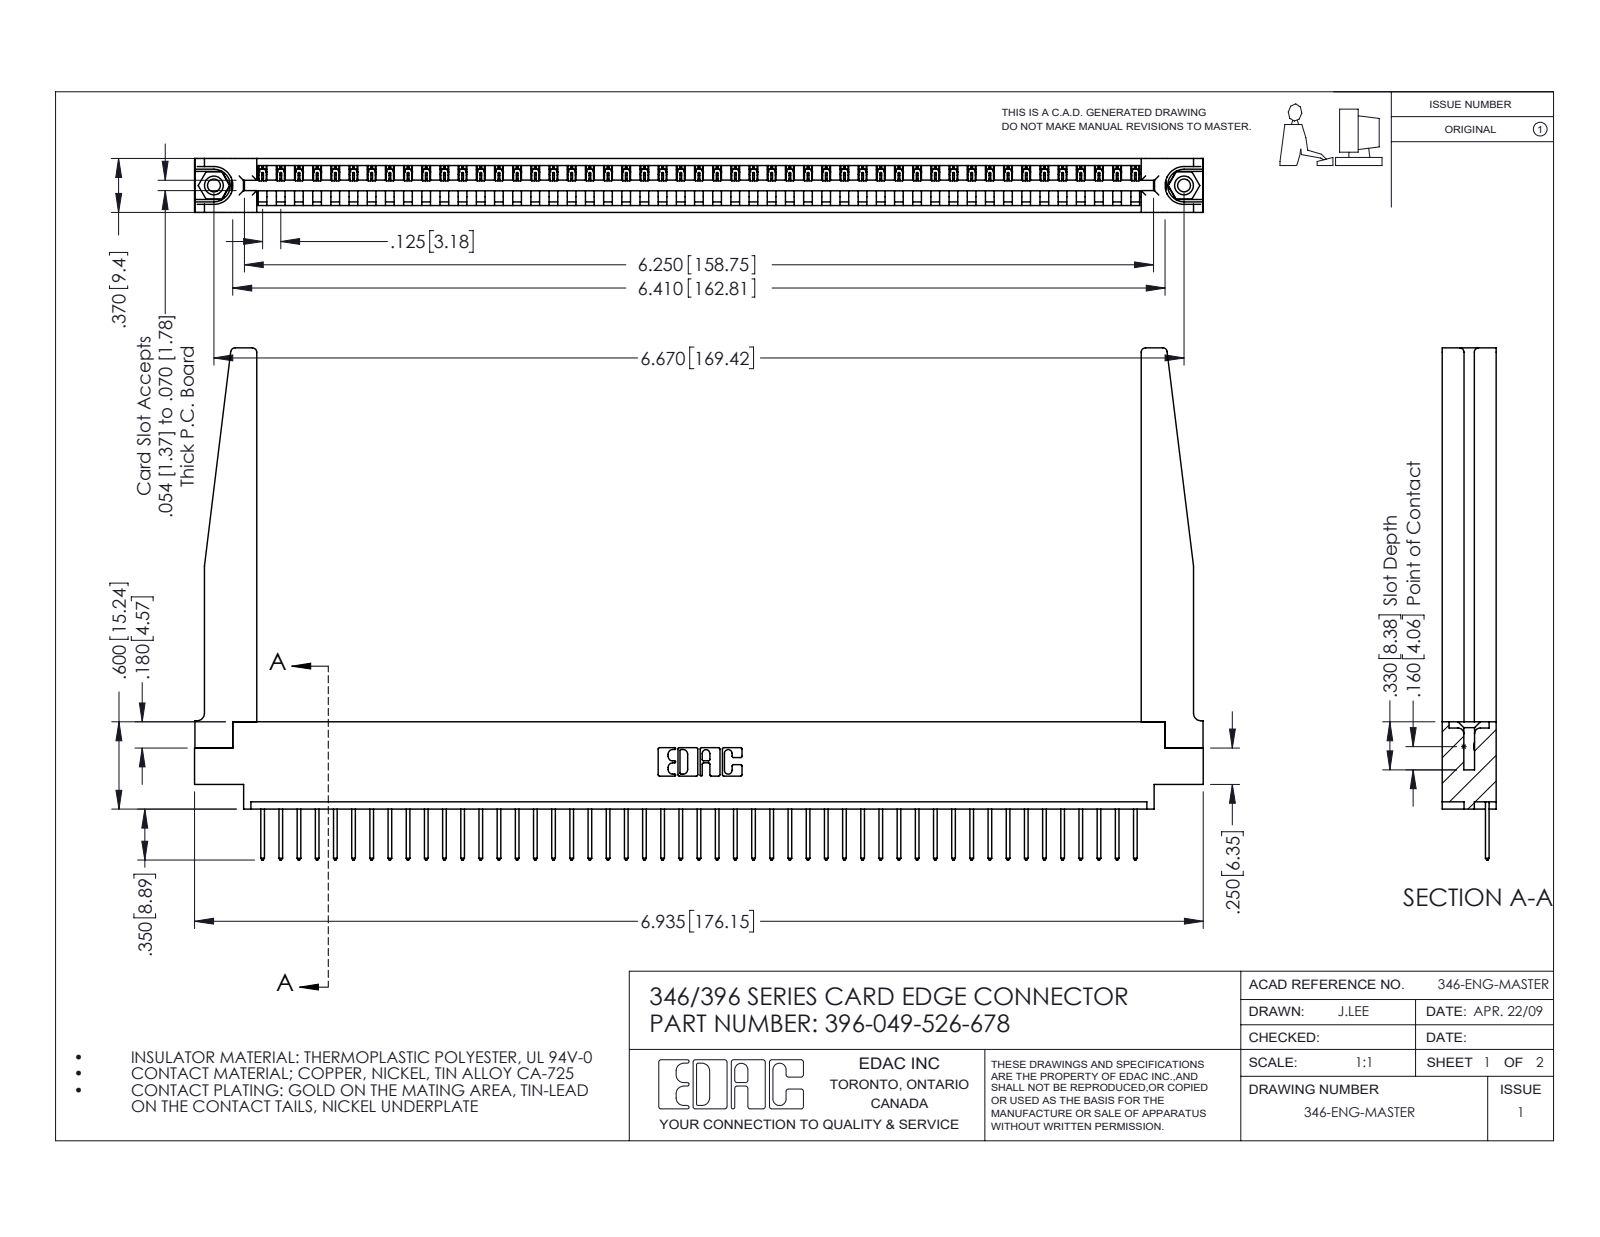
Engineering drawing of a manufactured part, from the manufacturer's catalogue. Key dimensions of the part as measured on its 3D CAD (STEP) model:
Part name (STEP PRODUCT): 346 Part_0.170 Offset - 0.156 Dia-TH; 346-220-078_345-220-078; 345-292-001_345-293-126; 345-250-001_345-250-001-102 (+1 more)
STEP written by: SolidWorks 2016 (CONFIG_CONTROL_DESIGN)
Units: inches
Bodies: 54 solids, 3202 faces (2182 planar, 968 cylindrical, 52 other)
Overall size (bounding box): 6.935 × 3.52 × 0.37
Volume: 1.442 in³ · Surface area: 42.81 in²
Round holes (diameter × count): ⌀0.089 ×2, ⌀0.125 ×2, ⌀0.156 ×2, ⌀0.064 ×1
Round bosses / shafts (diameter × count): ⌀0.155 ×2
Partial cylindrical surfaces — rounded edges, fillets, slot ends (radius × count): R0.006 ×98, R0.01 ×98, R0.01 ×22, R0.03 ×8, R0.007 ×6, R0.031 ×6, R0.026 ×3, R0.031 ×2
Main face-to-face distances: 0.37, 0.048, 0.322, 0.072, 0.25, 0.148, 0.15, 0.298, 0.025, 0.222
Hole centre spacings: 0.246, 6.461, 6.67
